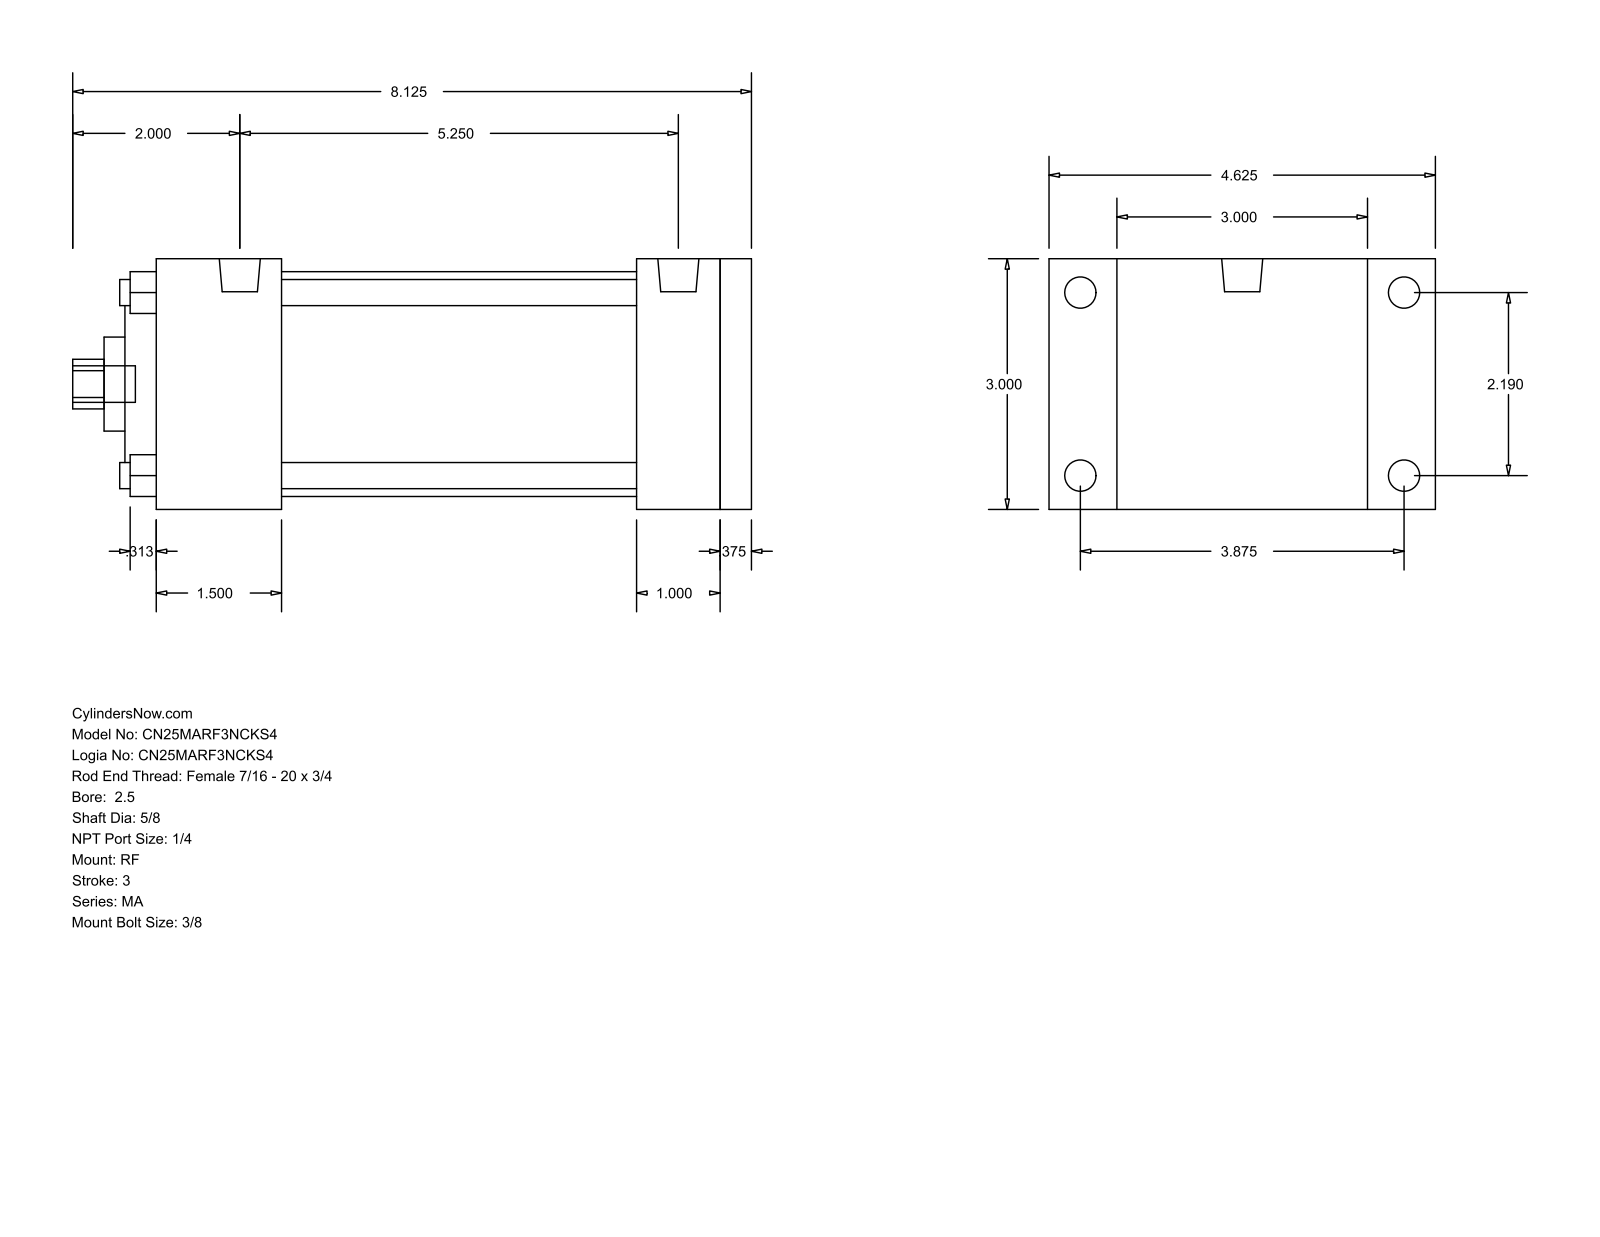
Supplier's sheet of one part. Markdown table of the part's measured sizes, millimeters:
| quantity | value |
| --- | --- |
| part name | MA_RF__0250_0.625 |
| STEP written by | GSSL Pune (CONFIG_CONTROL_DESIGN) |
| units | millimeters |
| bodies | 0 solids, 94 faces (65 planar, 29 cylindrical, 0 other) |
| overall size | 206.38 × 117.47 × 76.2 |
| round holes (diameter × count) | 7.94 × 4, 15.88 × 1, 28.57 × 1, 50.8 × 1, 68.33 × 1 |
| round bosses / shafts (diameter × count) | 9.53 × 4, 7.94 × 4, 12.49 × 2, 11.11 × 1 |
| partial cylindrical surfaces (radius × count) | 7.54 × 1 |
| main face-to-face distances | 76.2, 180.98, 9.53, 171.45, 25.4, 38.1, 146.05, 107.95, 133.35, 142.88 |
| hole center spacings | 39.33, 55.62, 78.66 |
